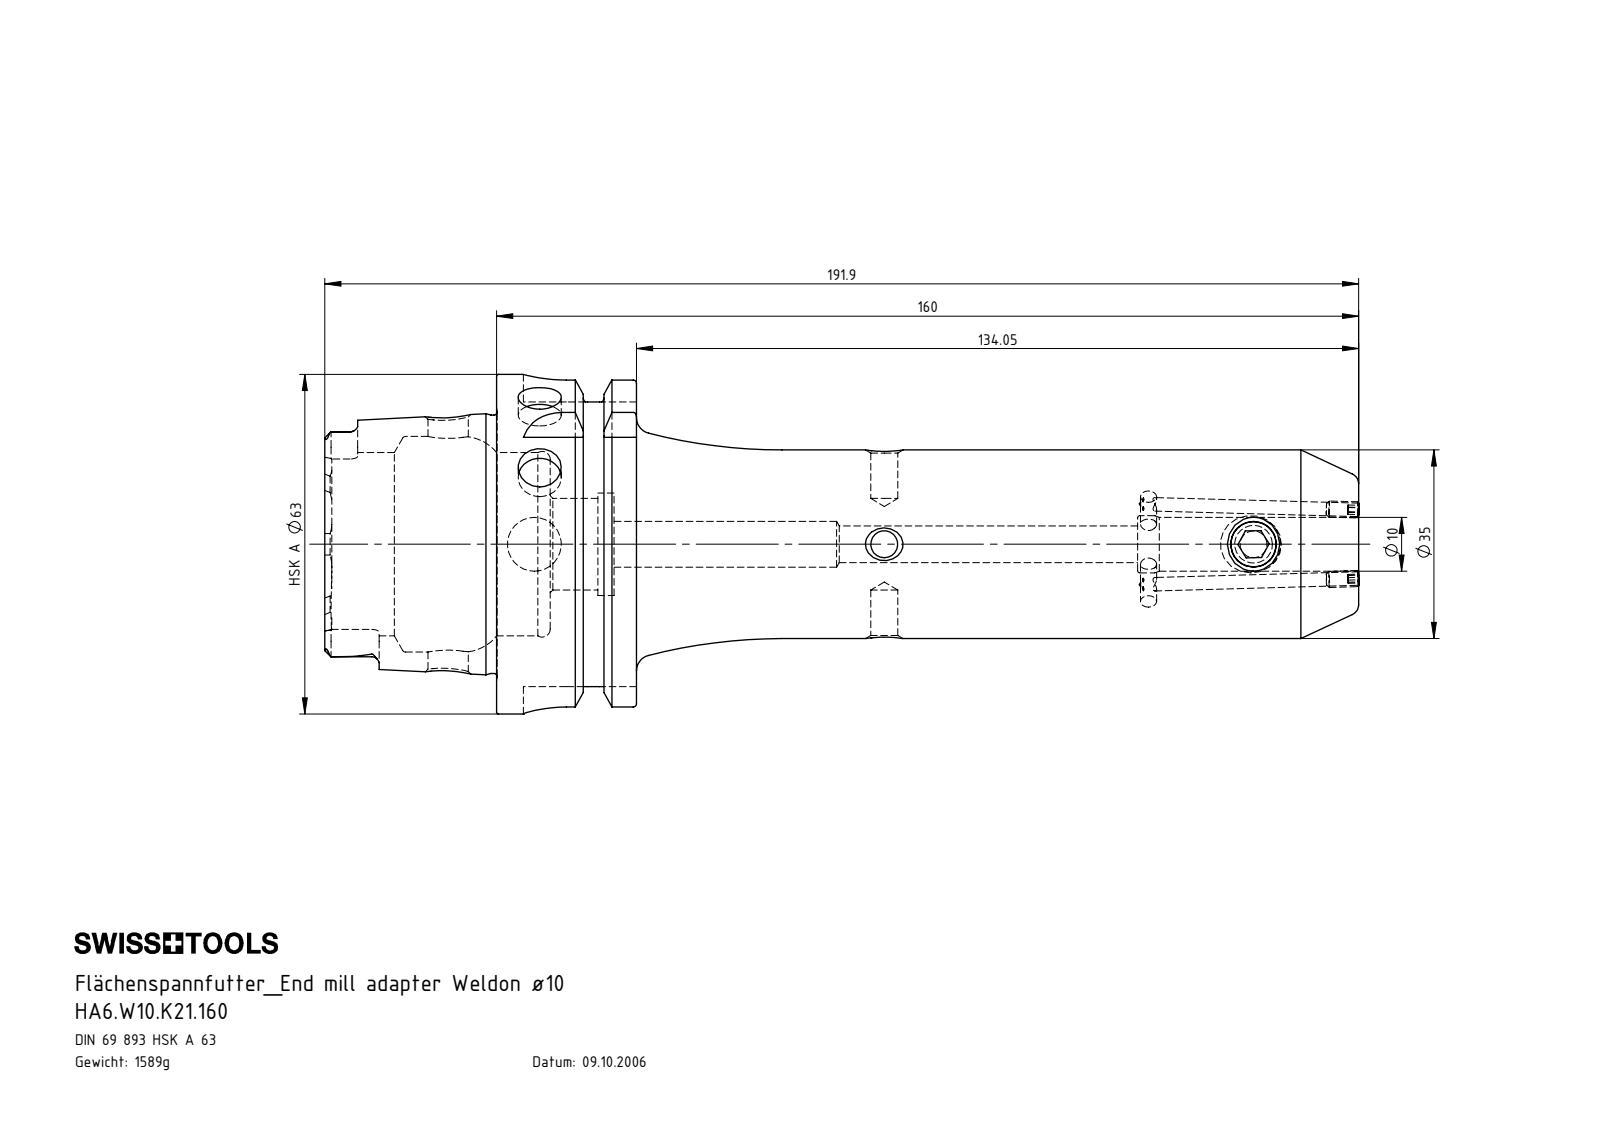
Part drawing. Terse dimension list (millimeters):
name: HA6.W10.K21.160; ERU-CJ2.001.006; W10-ER1.001.012; HA6-W10.K21.160_C_Fertigbearbeitung
written by: SolidWorks 2012 (CONFIG_CONTROL_DESIGN)
unit: mm
bodies: 4 solids, 292 faces (77 planar, 83 cylindrical, 132 other)
size: 191.98 × 63 × 63
volume: 202 407 mm³; area: 42 132 mm²
holes: 2× ⌀2.5, 2× ⌀5, 2× ⌀8, 2× ⌀8.5, 2× ⌀10, 1× ⌀3, 1× ⌀6.8, 1× ⌀7.5, 1× ⌀10.6, 1× ⌀17, 1× ⌀19, 1× ⌀34
bosses: 2× ⌀3, 1× ⌀63, 1× ⌀54.95, 1× ⌀47.94, 1× ⌀35, 1× ⌀10
rounds: 6× R1.4, 4× R2.88, 4× R8
face distances: 25.95, 16, 9.95, 31.9, 41.85, 57.85, 52.8, 191.9, 160, 150.05
hole spacings: 64.95, 68.55, 80.95, 133.5
